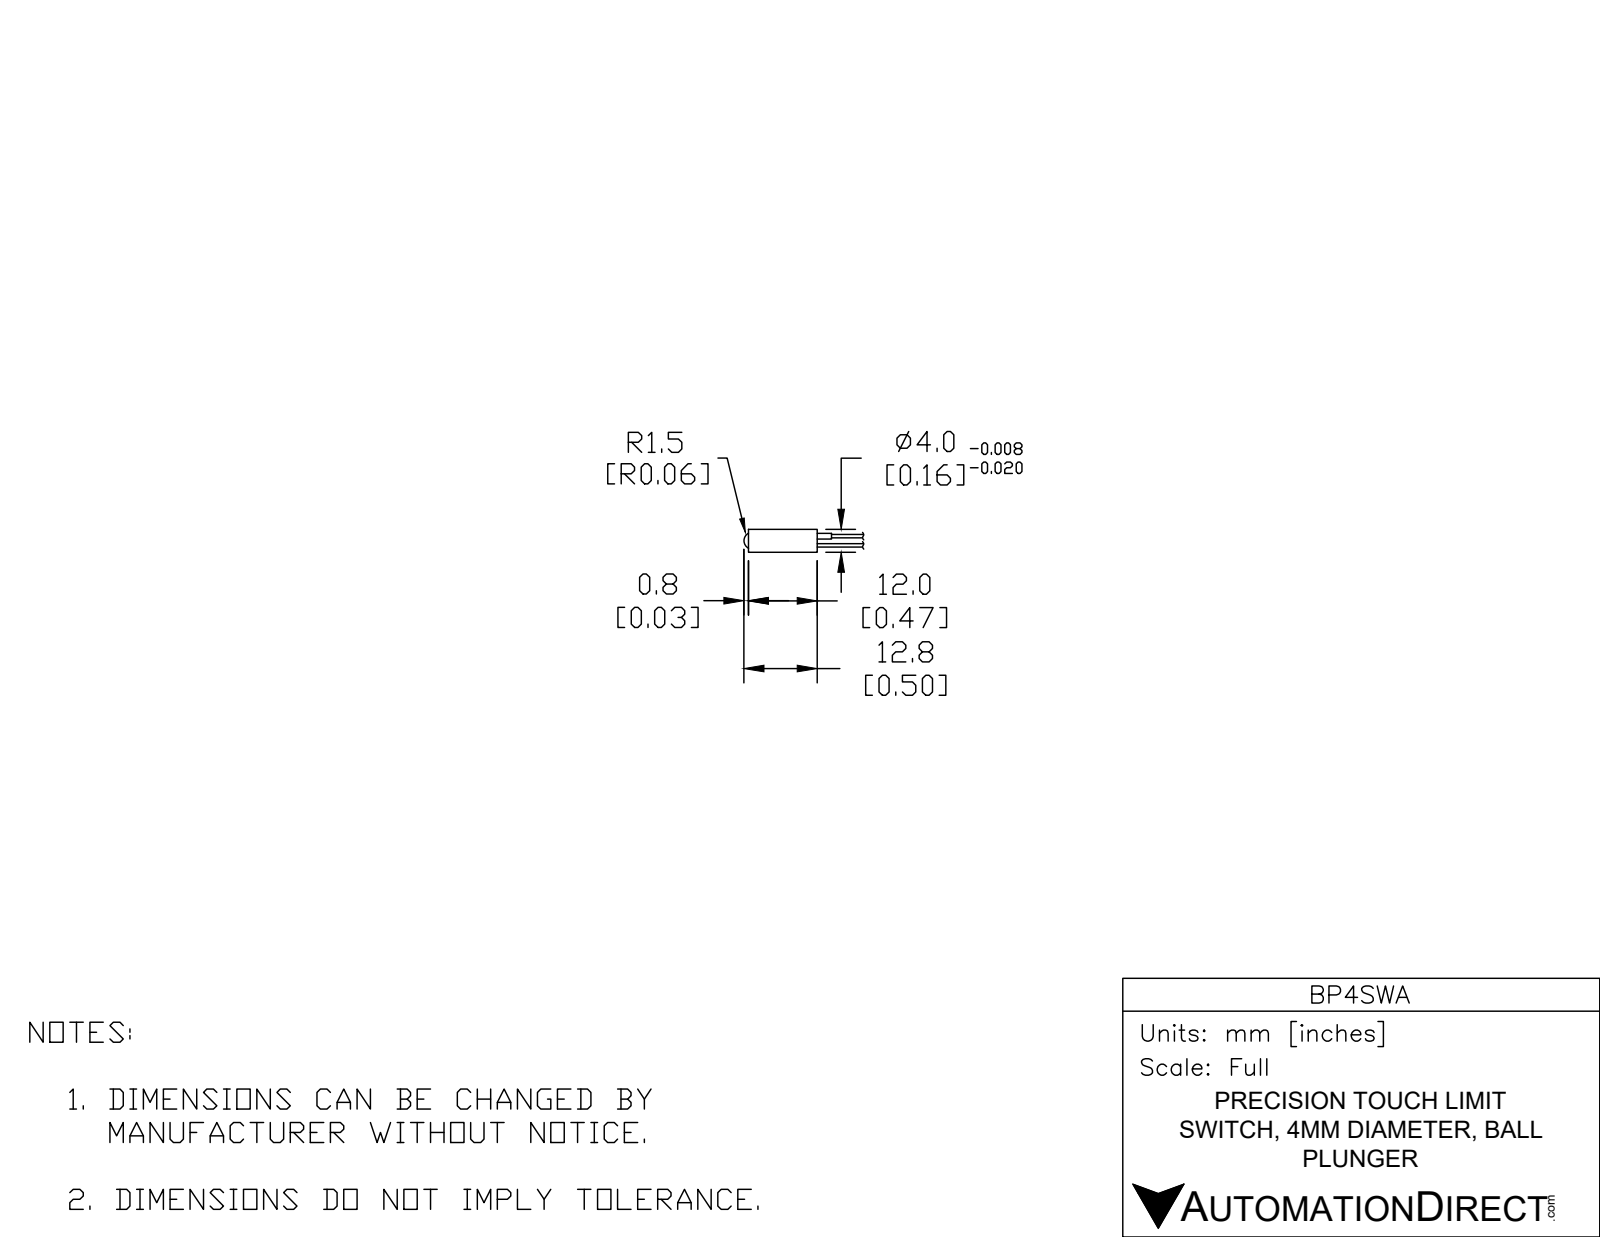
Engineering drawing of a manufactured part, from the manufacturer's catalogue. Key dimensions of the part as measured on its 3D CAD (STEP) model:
STEP written by: Spatial InterOp 3D (CONFIG_CONTROL_DESIGN)
Units: millimetres
Bodies: 1 solid, 15 faces (5 planar, 8 cylindrical, 2 other)
Overall size (bounding box): 22.8 × 4 × 4
Volume: 160 mm³ · Surface area: 219 mm²
Round bosses / shafts (diameter × count): ⌀0.6 ×2, ⌀4 ×1, ⌀1 ×1
Main face-to-face distances: 12, 22, 10, 14.5, 2.5, 7.5
